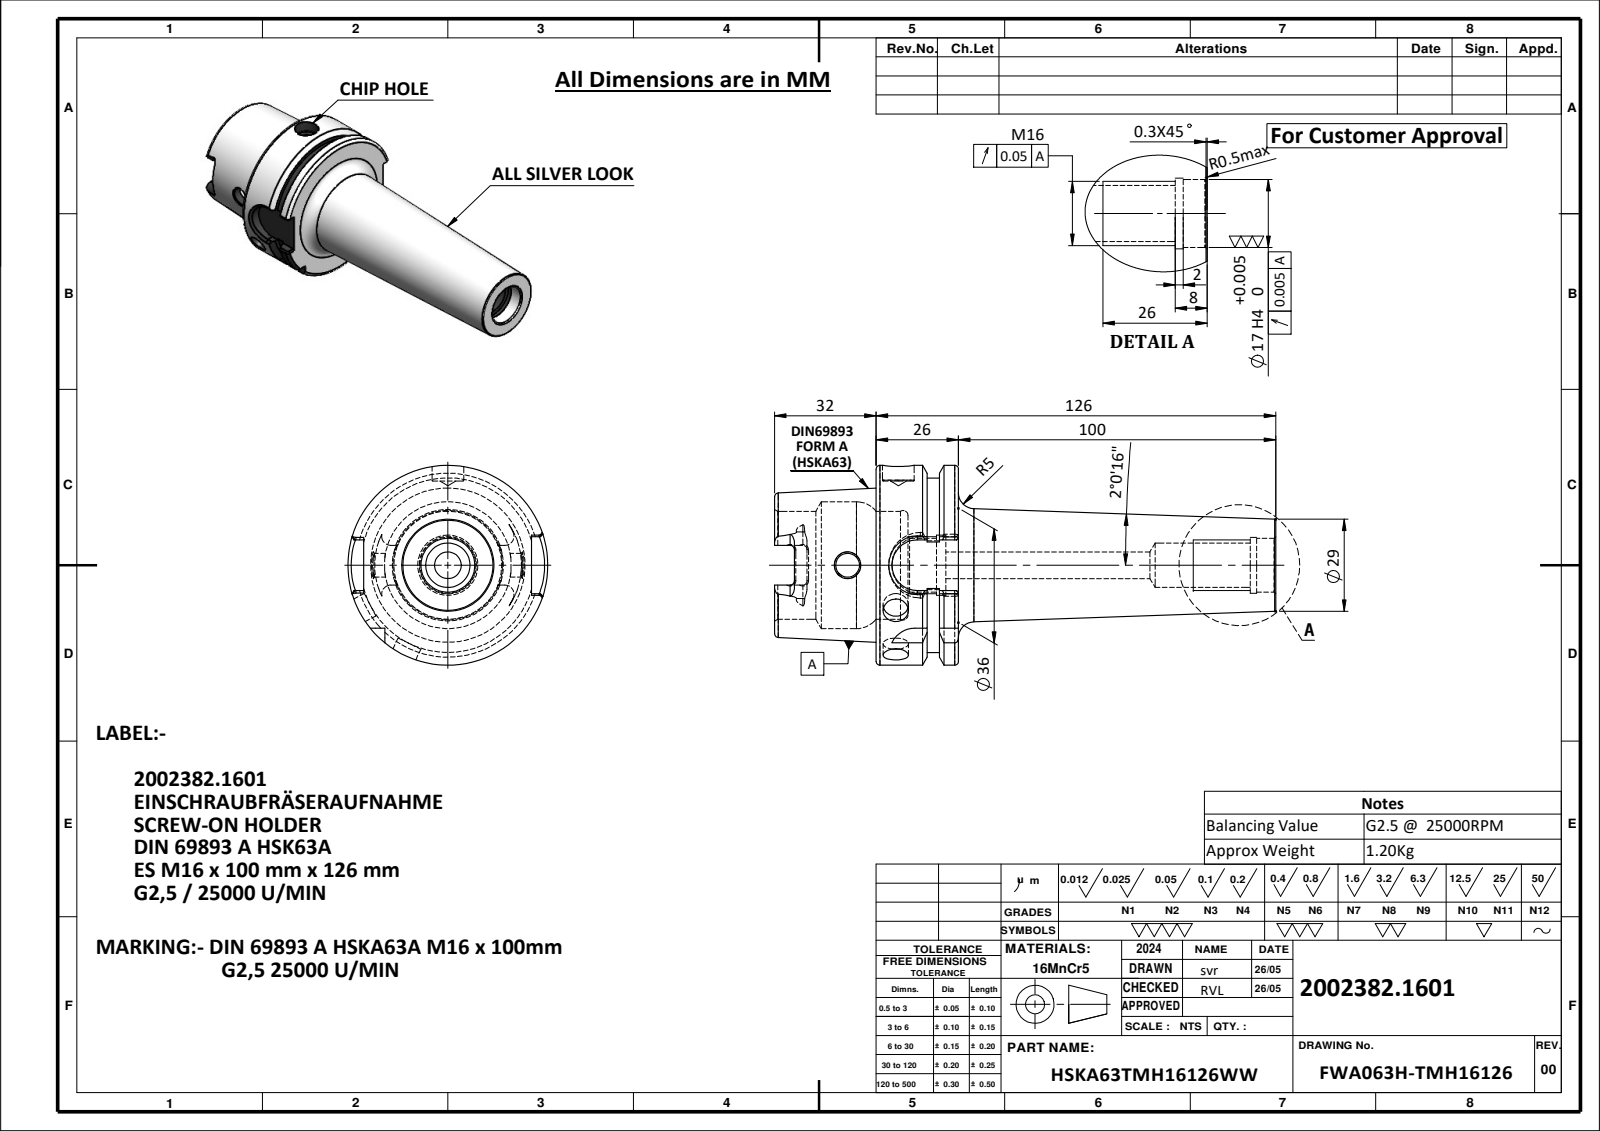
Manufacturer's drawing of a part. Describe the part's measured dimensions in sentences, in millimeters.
The part is named "HSKA63TMS16126WW; FWA063H-TMH16126". Its 3-D file was written by "SolidWorks 2024 (CONFIG_CONTROL_DESIGN)". It is 1 solid with 168 faces: 51 planar, 51 cylindrical and 66 other. Overall it measures 157.95 by 63 by 63 millimeters. Its volume is 154 695 cubic millimeters and its surface area 35 349 square millimeters. Round holes: 2 of diameter 8, 1 of diameter 7.5, 1 of diameter 8.4, 1 of diameter 10, 1 of diameter 14, 1 of diameter 17, 1 of diameter 17.6, 1 of diameter 19, 1 of diameter 34, 1 of diameter 40. Round bosses or shafts: 1 of diameter 63, 1 of diameter 55. Partial cylindrical surfaces (rounded edges, fillets, slot ends): 6 of radius 1.3, 4 of radius 2.88, 2 of radius 8, 1 of radius 9. The main face-to-face distances are 25.95, 10, 15.95, 32, 42, 57.95, 157.95, 125.95, 115.95, 100.
